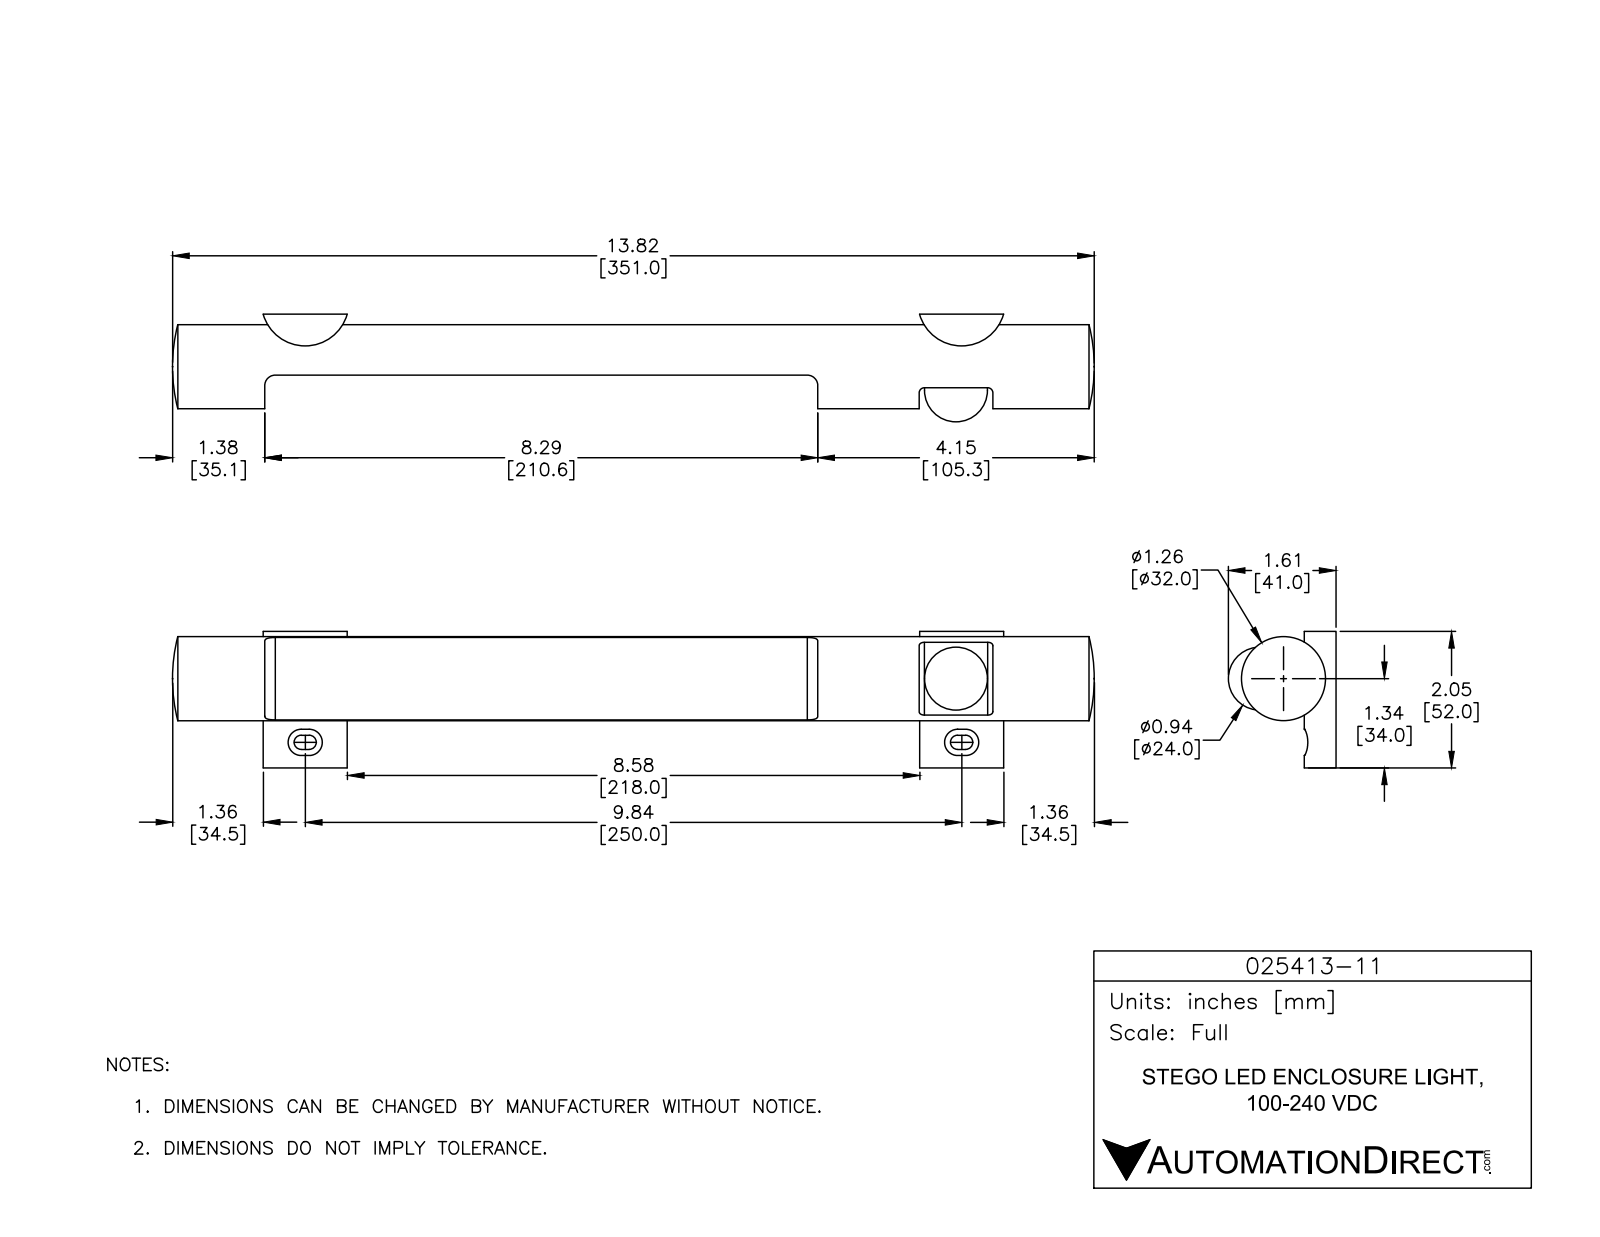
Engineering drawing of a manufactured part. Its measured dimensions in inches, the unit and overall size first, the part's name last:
Units: inches
Overall size (bounding box): 13.819 × 2.047 × 1.614
Round bosses / shafts (diameter × count): ⌀1.26 ×1
Partial cylindrical surfaces — rounded edges, fillets, slot ends (radius × count): R0.106 ×4, R0.197 ×4, R0.079 ×2, R0.157 ×2, R0.655 ×2
Main face-to-face distances: 0.913, 2.047, 1.102, 0.189, 8.291, 0.079, 0.835, 1.024, 10.917, 2.626
Volume: 14.58 in³ · Surface area: 64.36 in²
Bodies: 1 solid, 44 faces (22 planar, 16 cylindrical, 6 other)
Part name (STEP PRODUCT): PRODUCT_NAME_1
STEP written by: ACIS (CONFIG_CONTROL_DESIGN)
